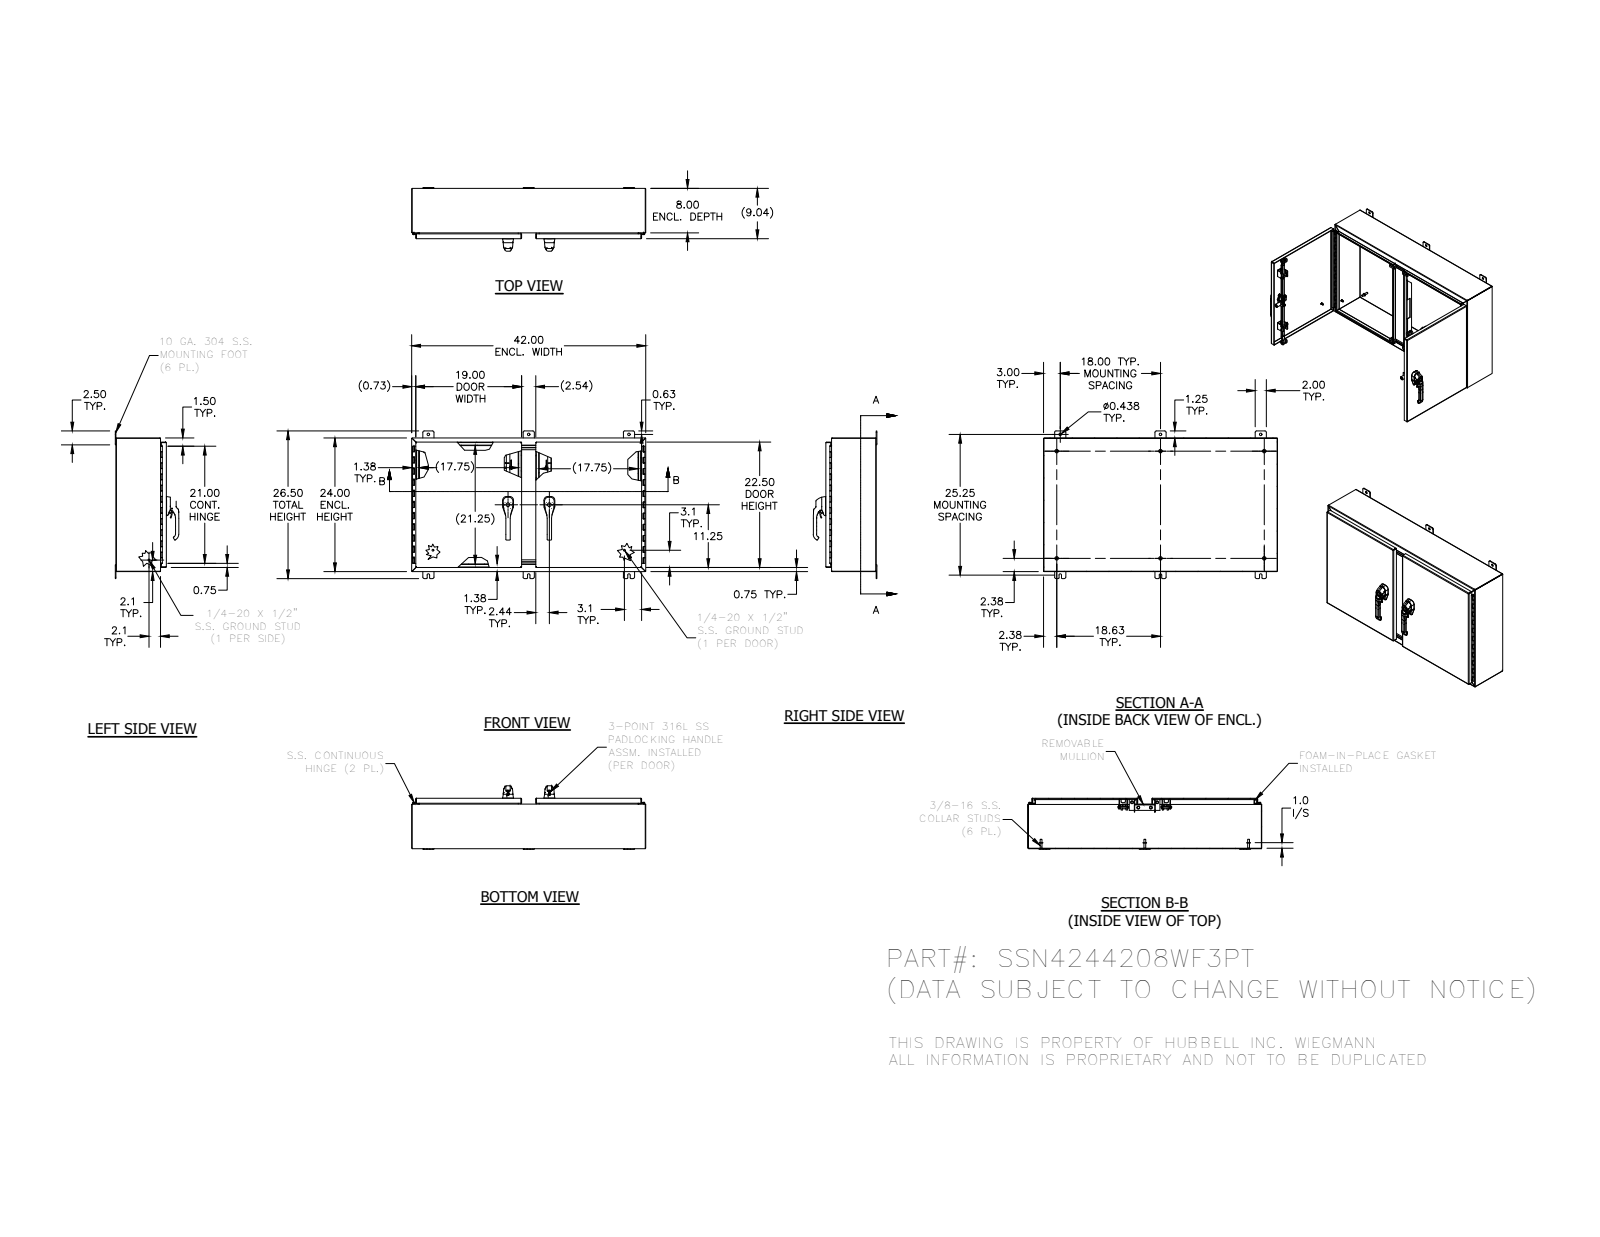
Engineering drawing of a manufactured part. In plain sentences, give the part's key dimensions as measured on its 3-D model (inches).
The part is named "38859; DIN985_M10; HFW31712; PLASTIC-ROLLER-CAM_AF0_ASM (+8 more)". Its 3-D file was written by "SolidWorks 2014 (AUTOMOTIVE_DESIGN)". It is 125 solids with 6344 faces: 2242 planar, 2586 cylindrical and 1516 other. Overall it measures 42 by 26.5 by 11.409 inches. Its volume is 328.1 cubic inches and its surface area 7 942 square inches. Round holes: 12 of diameter 0.262, 8 of diameter 0.187, 6 of diameter 0.213, 6 of diameter 0.28, 6 of diameter 0.438, 4 of diameter 0.196, 4 of diameter 0.252, 4 of diameter 0.281, 4 of diameter 0.315, 4 of diameter 0.4, 4 of diameter 0.402, 4 of diameter 0.45. Round bosses or shafts: 9 of diameter 0.25, 6 of diameter 0.625, 6 of diameter 0.533, 6 of diameter 0.33, 5 of diameter 0.236, 4 of diameter 0.531, 4 of diameter 0.438, 4 of diameter 0.435. Partial cylindrical surfaces (rounded edges, fillets, slot ends): 317 of radius 0.02, 221 of radius 0.012, 39 of radius 0.019, 33 of radius 0.031, 31 of radius 0.125, 30 of radius 0.05, 30 of radius 0.25, 25 of radius 0.079. The main face-to-face distances are 0.074, 0.094, 8.942, 8.868, 9.035, 8.961, 23.926, 7.926, 41.926, 23.852. The hole center spacings are 0.38, 0.76, 7.417, 0.492, 0.492, 0.886, 1.236, 1.376.
